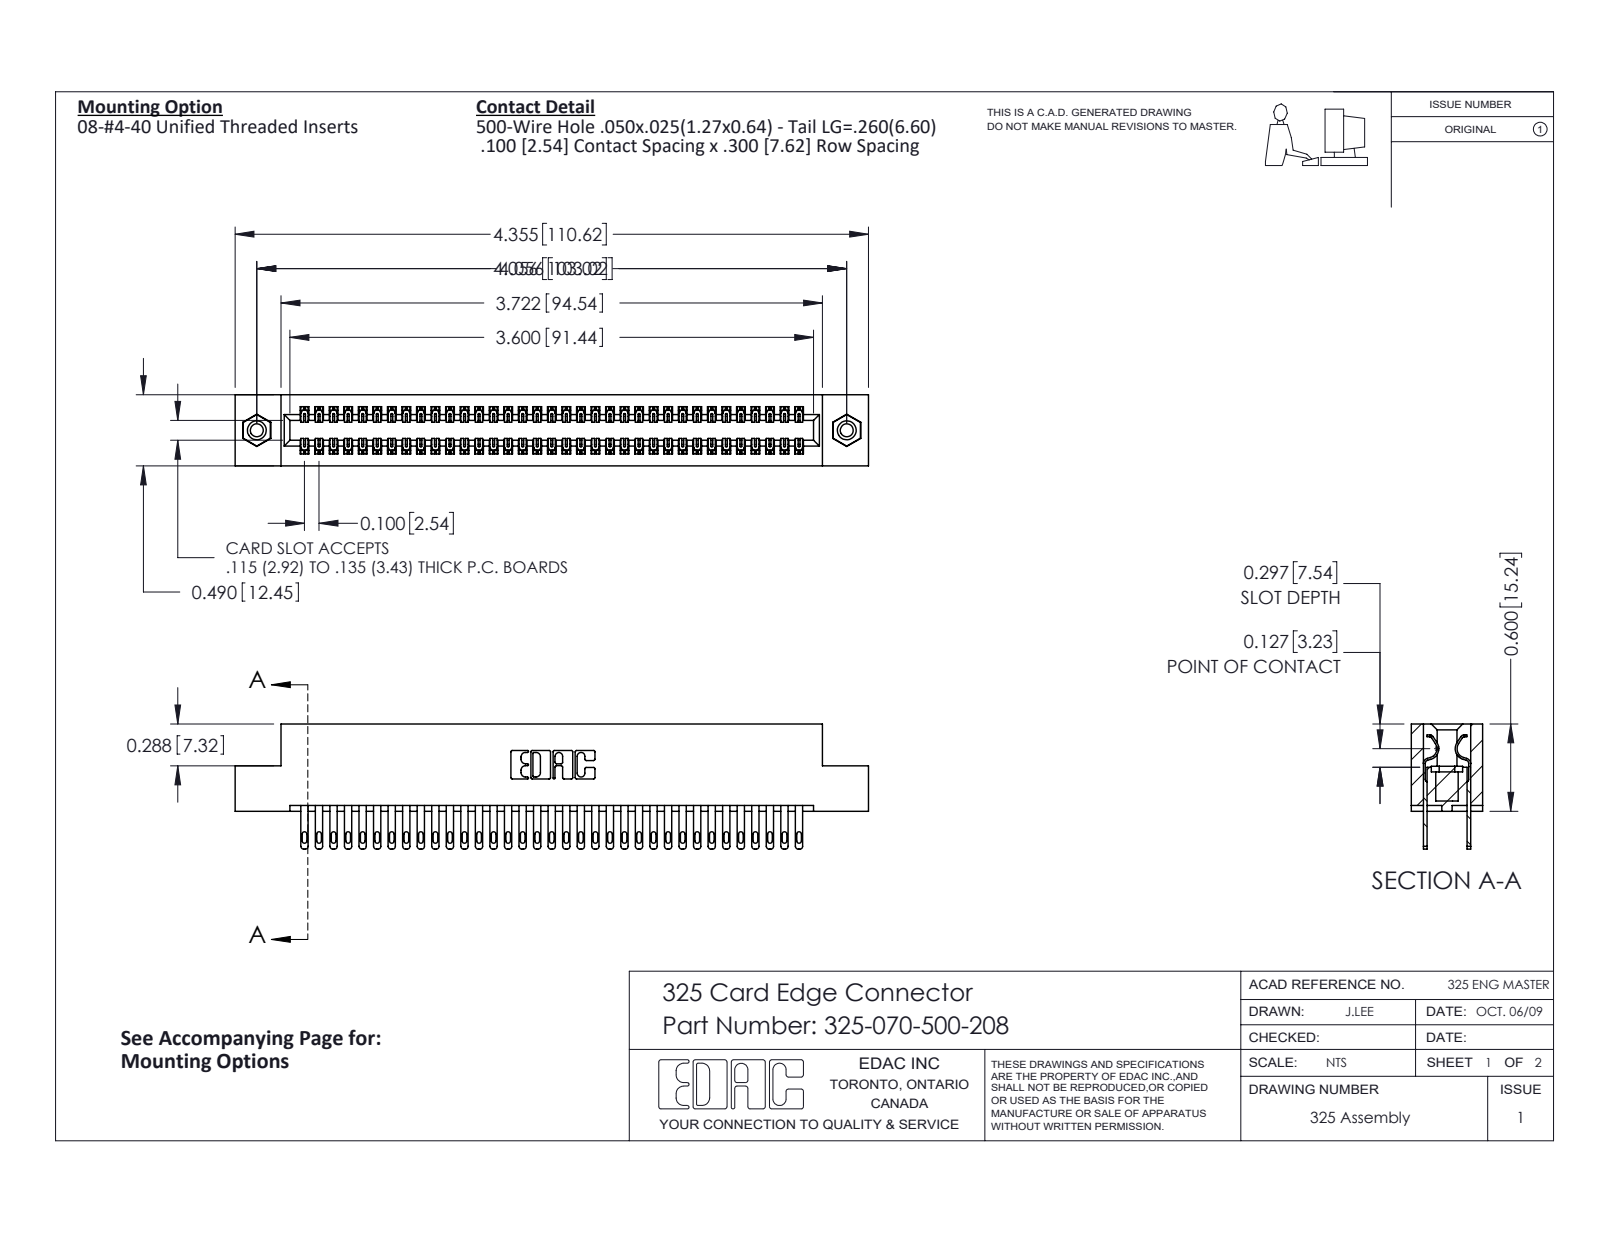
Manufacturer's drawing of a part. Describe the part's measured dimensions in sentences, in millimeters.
The part is named "325-292-001_325-293-100; 325 Part_TI; 325-070-500-208; 345-250-001_345-250-003-102". Its 3-D file was written by "SolidWorks 2016 (CONFIG_CONTROL_DESIGN)". It is 73 solids with 3534 faces: 2202 planar, 1316 cylindrical and 16 other. Overall it measures 110.6 by 21.8 by 12.4 millimeters. Its volume is 14 400 cubic millimeters and its surface area 18 040 square millimeters. Round holes: 2 of diameter 2.3, 2 of diameter 3.2, 2 of diameter 4.1. Round bosses or shafts: 2 of diameter 3.9. Partial cylindrical surfaces (rounded edges, fillets, slot ends): 105 of radius 0.2, 70 of radius 0.4, 70 of radius 0.5, 22 of radius 0.3, 6 of radius 0.2, 6 of radius 0.8, 3 of radius 0.7, 2 of radius 0.4. The main face-to-face distances are 2.1, 10.3, 7.6, 2.7, 9.7, 0.6, 12.4, 8.3, 7, 14.2. The hole center spacings are 103.
